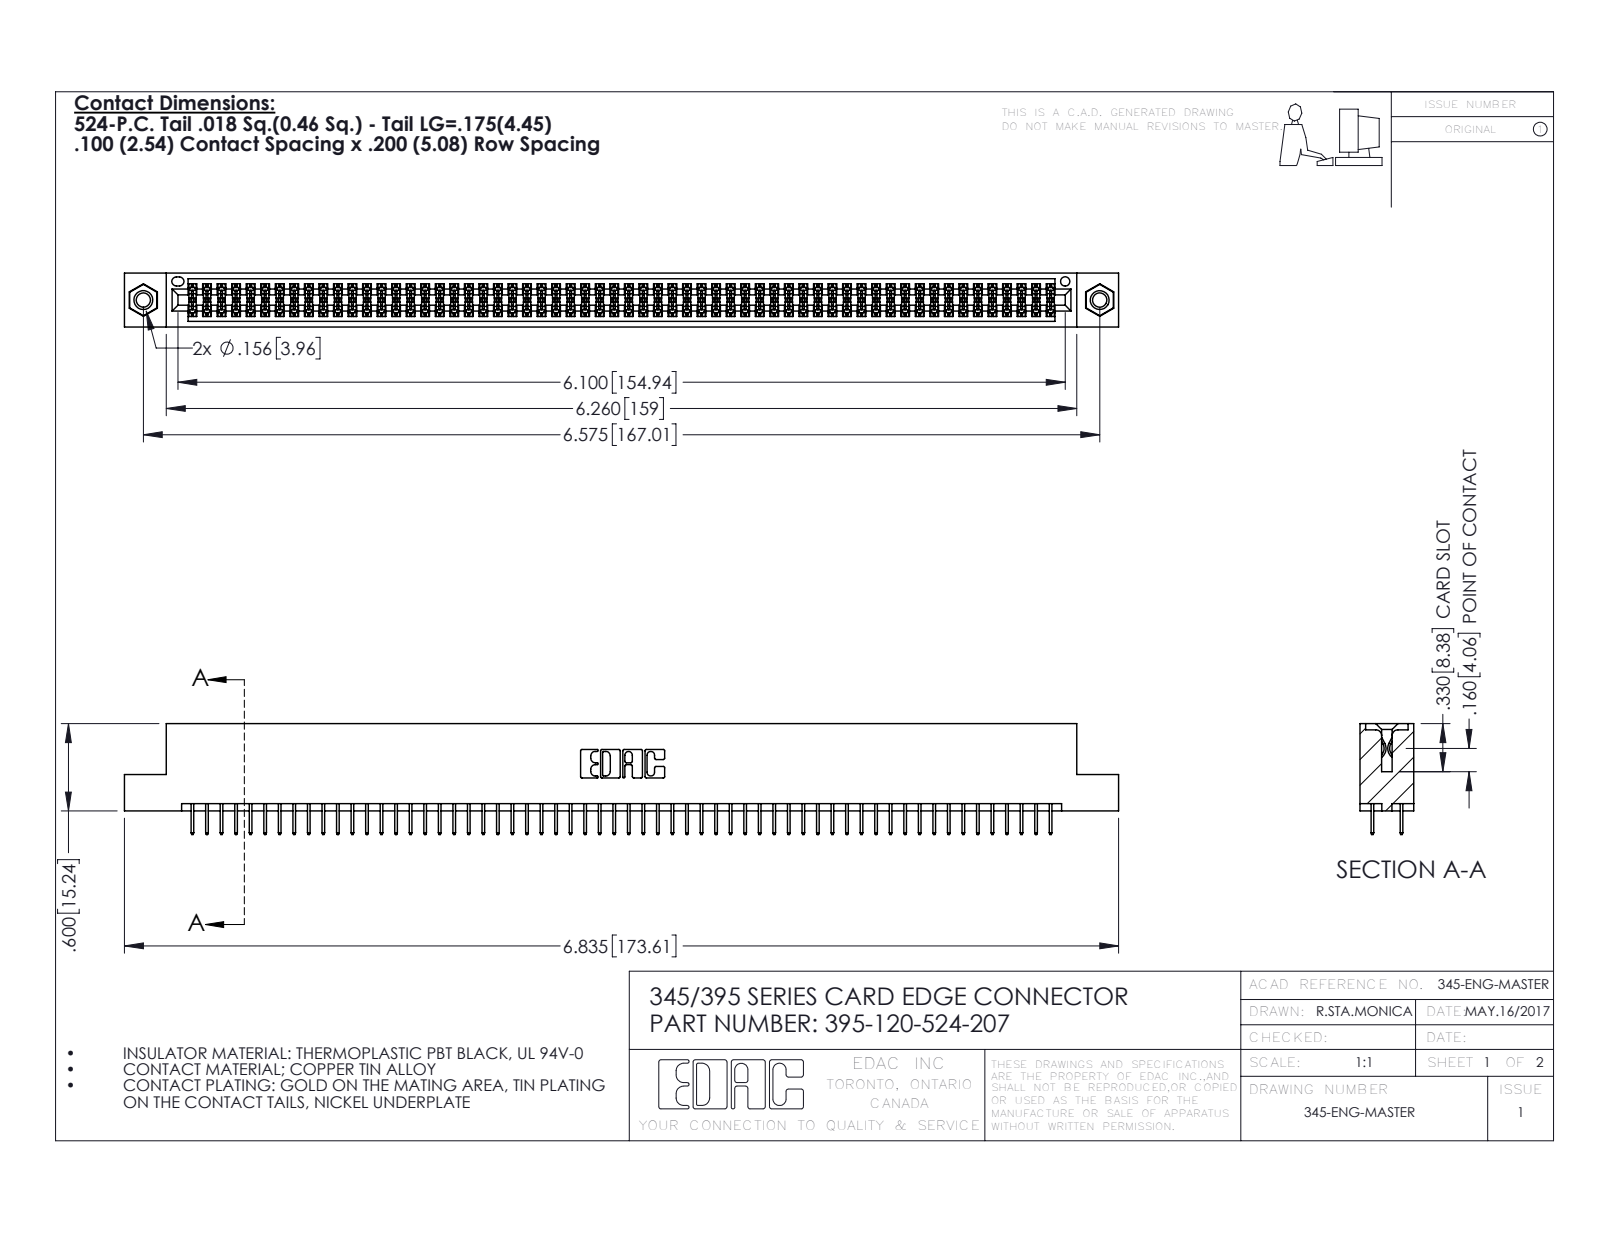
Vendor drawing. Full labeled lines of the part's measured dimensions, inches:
Part name (STEP PRODUCT): 345-292-001_345-293-124; 395-120-524-207; 345 Part_Flush Mounting Lugs - 0.156 Dia-TI; 345-250-001_345-250-005-103
STEP written by: SolidWorks 2016 (CONFIG_CONTROL_DESIGN)
Units: inches
Bodies: 123 solids, 6666 faces (4792 planar, 1858 cylindrical, 16 other)
Overall size (bounding box): 6.835 × 0.762 × 0.37
Volume: 1.027 in³ · Surface area: 38.42 in²
Round holes (diameter × count): ⌀0.098 ×2, ⌀0.125 ×2, ⌀0.156 ×2, ⌀0.064 ×1
Round bosses / shafts (diameter × count): ⌀0.155 ×2
Partial cylindrical surfaces — rounded edges, fillets, slot ends (radius × count): R0.006 ×180, R0.01 ×22, R0.007 ×6, R0.031 ×6, R0.026 ×3, R0.014 ×2, R0.019 ×2, R0.022 ×2
Main face-to-face distances: 0.072, 0.298, 0.2, 0.37, 0.098, 0.272, 0.025, 0.225, 0.072, 0.175
Hole centre spacings: 0.27, 6.339, 6.575
